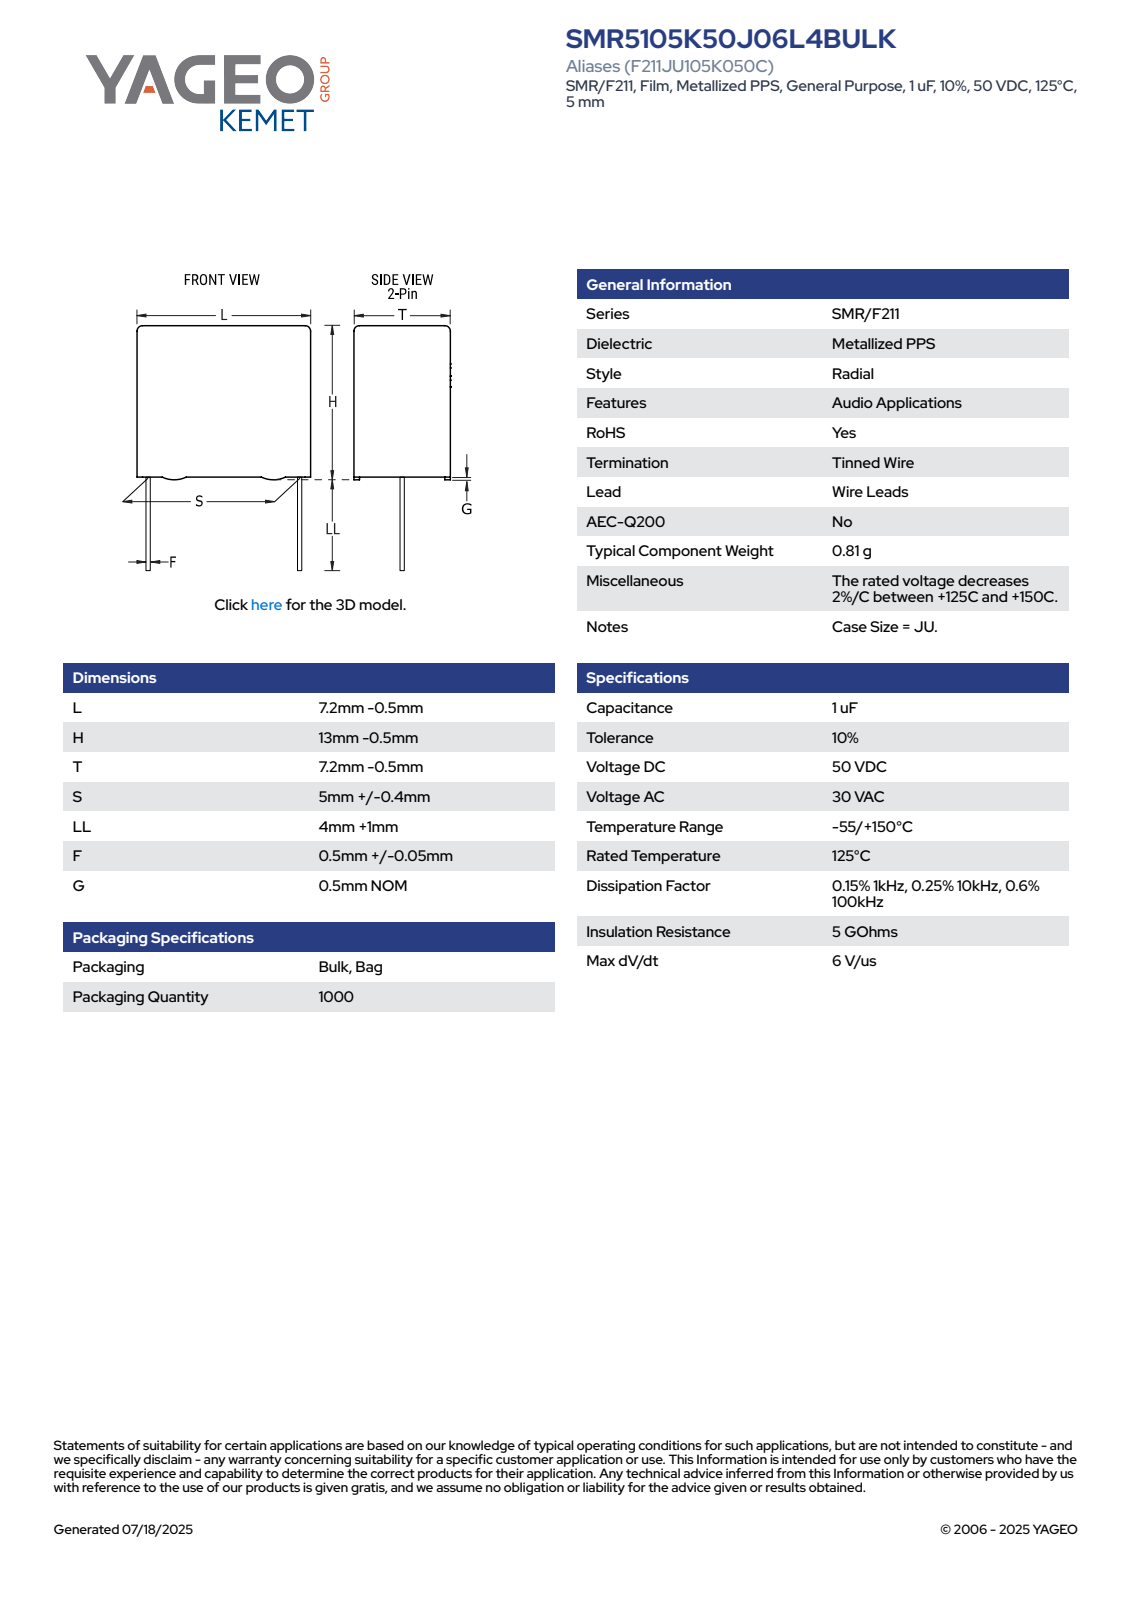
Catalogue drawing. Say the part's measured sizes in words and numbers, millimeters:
The part is named "CFR_RBG_7.2X13X7.2_L6.7H12.5T6.7S5LL5F0.55G0.5". Its 3-D file was written by "SolidWorks 2021 (AUTOMOTIVE_DESIGN)". It is 4 solids with 89 faces: 81 planar, 8 cylindrical and 0 other. Overall it measures 17.5 by 6.71 by 6.7 millimeters. Its volume is 541 cubic millimeters and its surface area 435 square millimeters. Round bosses or shafts: 2 of diameter 0.55. Partial cylindrical surfaces (rounded edges, fillets, slot ends): 4 of radius 0.5. The main face-to-face distances are 6.7, 12, 6.32, 0.38, 0.5, 12.5, 6.71, 6.33, 0.39, 5.94.
